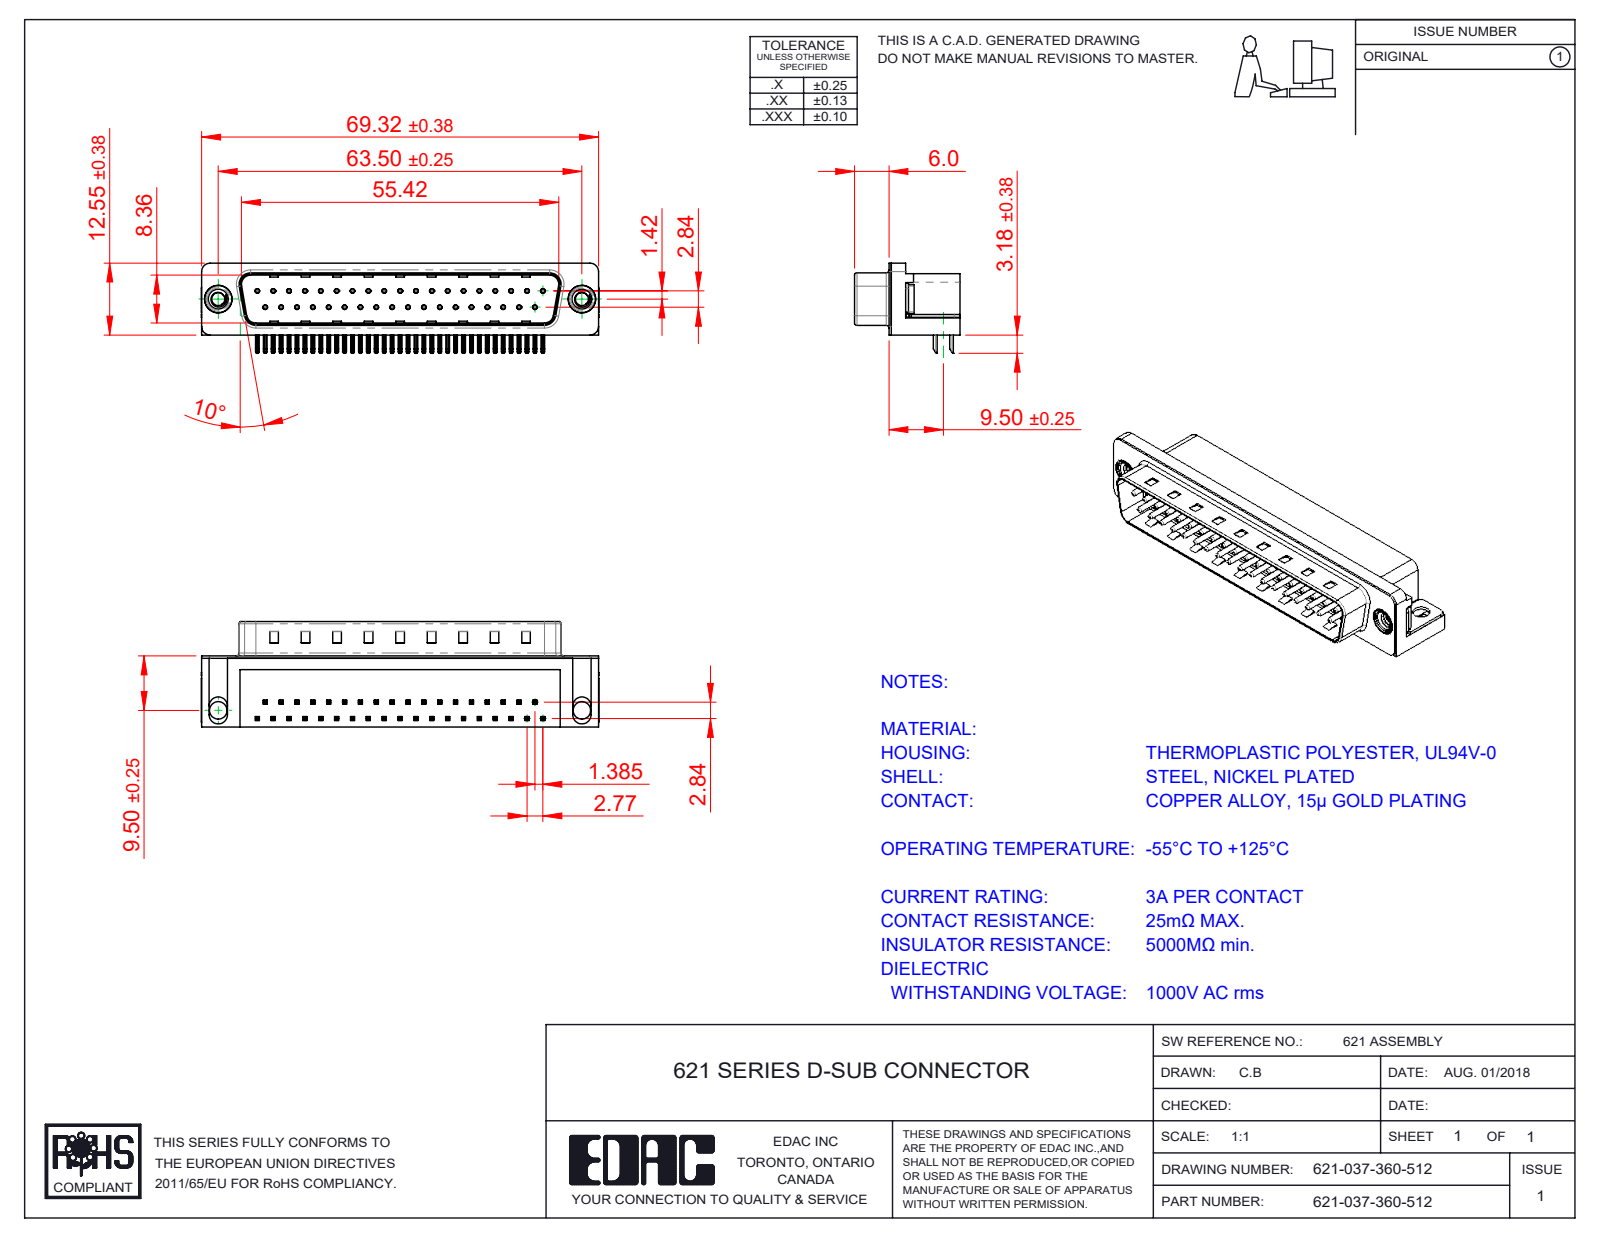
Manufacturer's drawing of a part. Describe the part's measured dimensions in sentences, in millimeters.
The part is named "621 Contact Top; 621 Thru Hole Board Mount; 621 Shell_37 Socket; 621-037-360-512 (+3 more)". Its 3-D file was written by "SolidWorks 2016 (CONFIG_CONTROL_DESIGN)". It is 43 solids with 3197 faces: 2011 planar, 915 cylindrical and 271 other. Overall it measures 69.4 by 18.4 by 15.73 millimeters. Its volume is 8 620 cubic millimeters and its surface area 10 081 square millimeters. Round holes: 37 of diameter 0.35, 37 of diameter 0.8, 2 of diameter 2.26, 2 of diameter 3.05, 2 of diameter 4, 2 of diameter 4.8, 2 of diameter 5. Round bosses or shafts: 37 of diameter 0.75, 2 of diameter 4.9, 2 of diameter 4.75, 2 of diameter 3.9. Partial cylindrical surfaces (rounded edges, fillets, slot ends): 156 of radius 0.25, 74 of radius 0.12, 16 of radius 1, 9 of radius 0.5, 8 of radius 1.6, 7 of radius 1.5, 4 of radius 0.9, 4 of radius 2. The main face-to-face distances are 0.4, 12, 10.35, 8.76, 2.1, 1.7, 10.46, 10.86, 9, 12.4. The hole center spacings are 3.16, 2.77, 5.54, 8.31, 11.08, 13.85, 19.39, 22.16.
